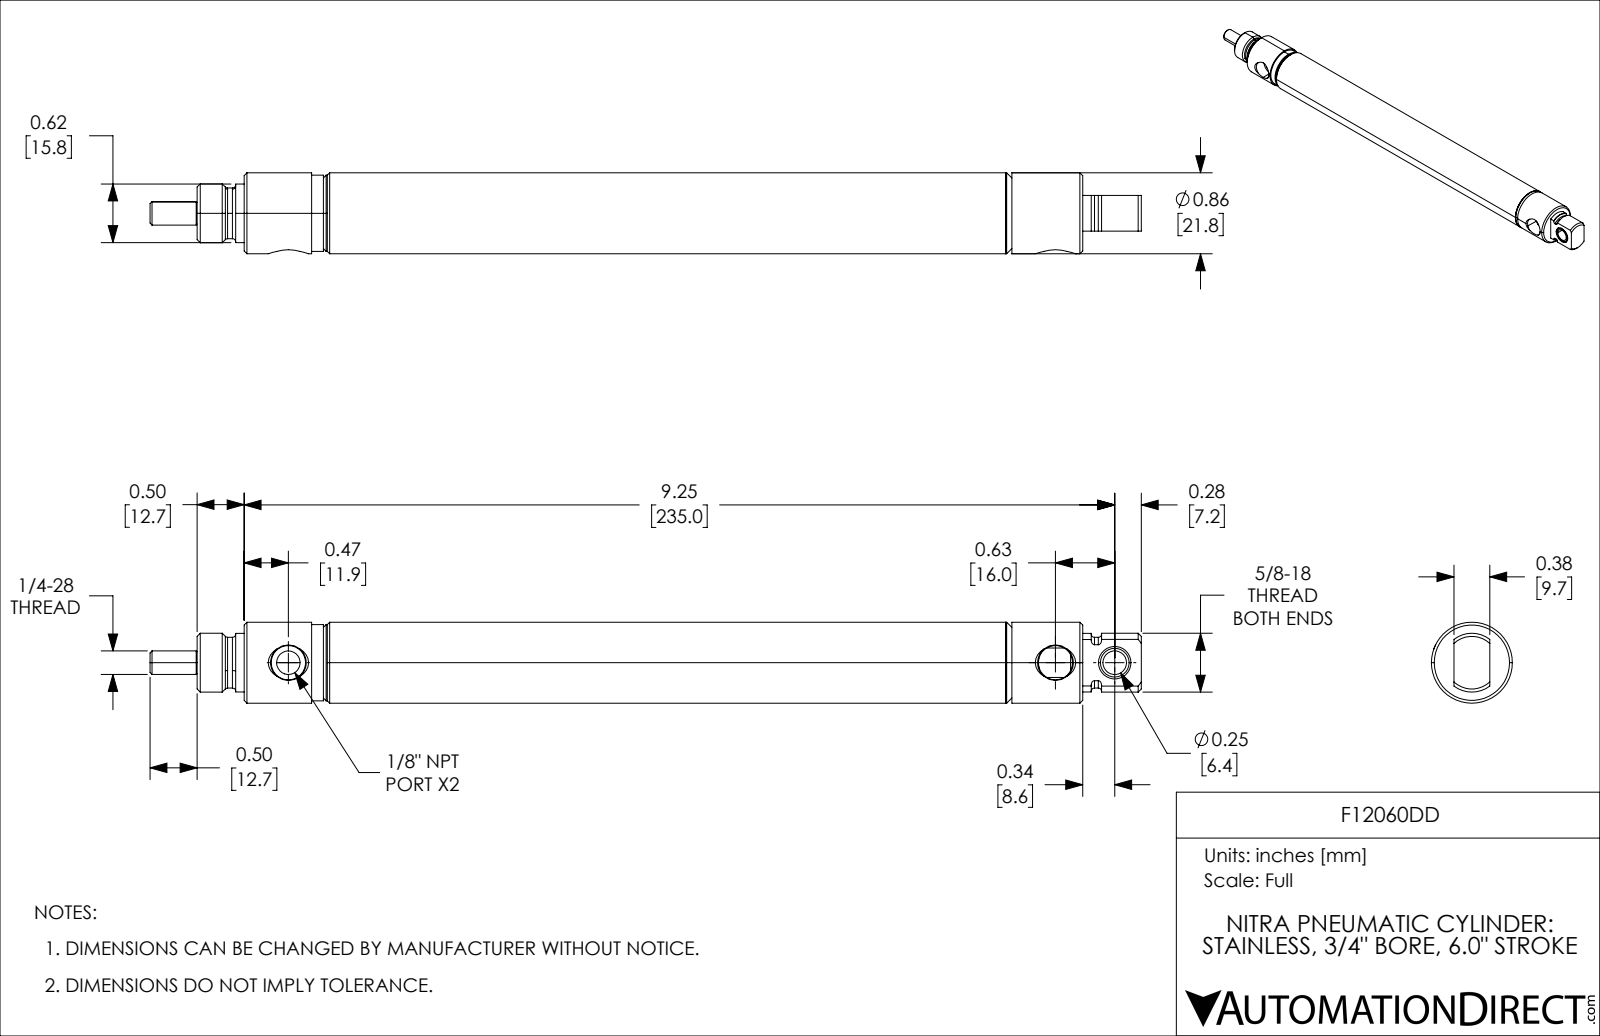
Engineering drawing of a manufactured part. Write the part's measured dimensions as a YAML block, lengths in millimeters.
part_name: "F12060DD_9; F12060DD; F12060DD_5; F12060DD_3 (+2 more)"
step_written_by: "SolidWorks 2021 (CONFIG_CONTROL_DESIGN)"
units: millimeters
bodies: {solids: 5, faces: 158, planar: 29, cylindrical: 61, other: 68}
overall_size: [267.51, 21.84, 21.84]
volume: 46387
surface_area: 39201
round_holes:
  - {diameter: 6.35, count: 1}
  - {diameter: 6.38, count: 1}
  - {diameter: 6.95, count: 1}
  - {diameter: 7.92, count: 1}
  - {diameter: 8.78, count: 1}
  - {diameter: 9.23, count: 1}
  - {diameter: 12.7, count: 1}
  - {diameter: 17.83, count: 1}
round_bosses_or_shafts:
  - {diameter: 21.84, count: 1}
  - {diameter: 20.57, count: 1}
  - {diameter: 19.35, count: 1}
  - {diameter: 15.88, count: 1}
  - {diameter: 15.81, count: 1}
  - {diameter: 13.68, count: 1}
  - {diameter: 6.35, count: 1}
  - {diameter: 5.84, count: 1}
partial_cylinders:
  - {radius: 6.84, count: 1}
face_to_face_distances: [21.43, 40.49, 214.32, 152.4, 173.83, 198.52, 46.12, 24.69, 12.7, 9.66]
hole_center_spacings: [16, 207.01, 223.01]
